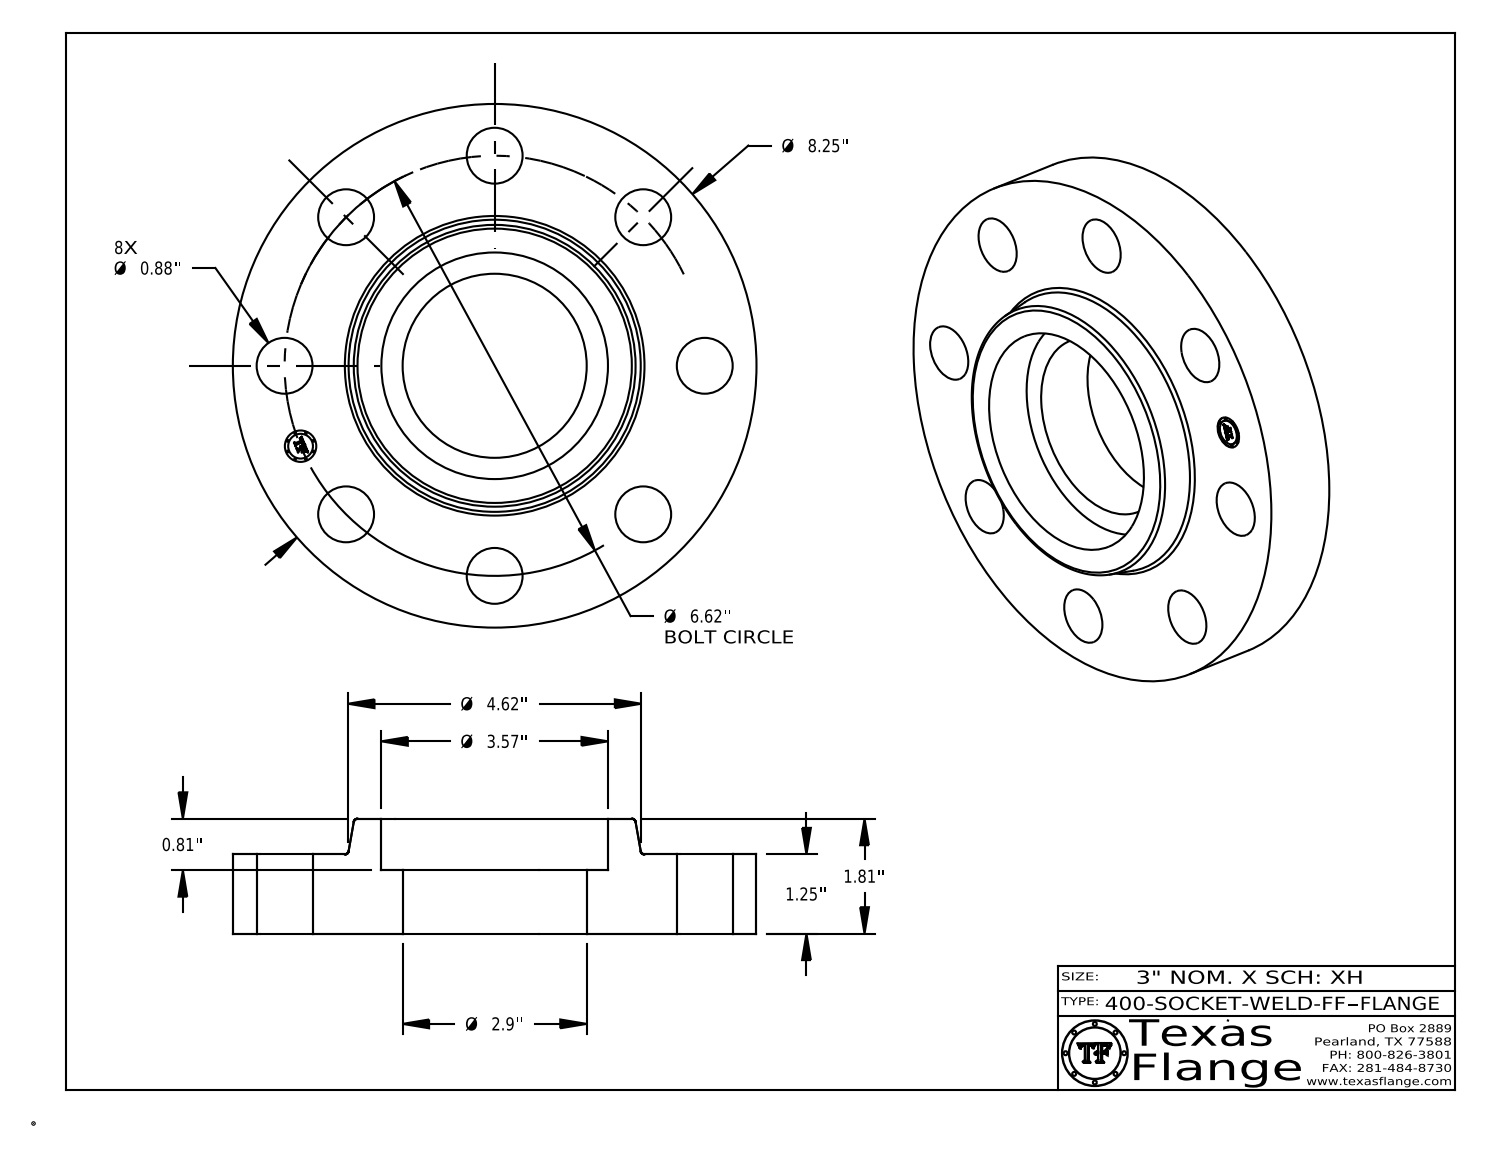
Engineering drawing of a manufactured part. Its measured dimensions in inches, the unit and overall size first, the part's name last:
Units: inches
Overall size (bounding box): 8.25 × 8.25 × 1.81
Round holes (diameter × count): ⌀0.88 ×8, ⌀0.495 ×1, ⌀2.9 ×1, ⌀3.57 ×1
Round bosses / shafts (diameter × count): ⌀0.03 ×8, ⌀8.25 ×1, ⌀0.39 ×1
Main face-to-face distances: 1.25, 1.81, 0.56, 1, 0.25, 0.81, 0.015, 1.235, 0.235, 0.575
Hole centre spacings: 3.31, 2.533, 6.116, 4.681, 4.681, 1.291, 3.678, 6.493
Volume: 55.02 in³ · Surface area: 168.5 in²
Bodies: 1 solid, 417 faces (369 planar, 42 cylindrical, 6 other)
Part name (STEP PRODUCT): 400-SOCKET-WELD-FF
STEP written by: CATIA V5 STEP AP214 (AUTOMOTIVE_DESIGN)
